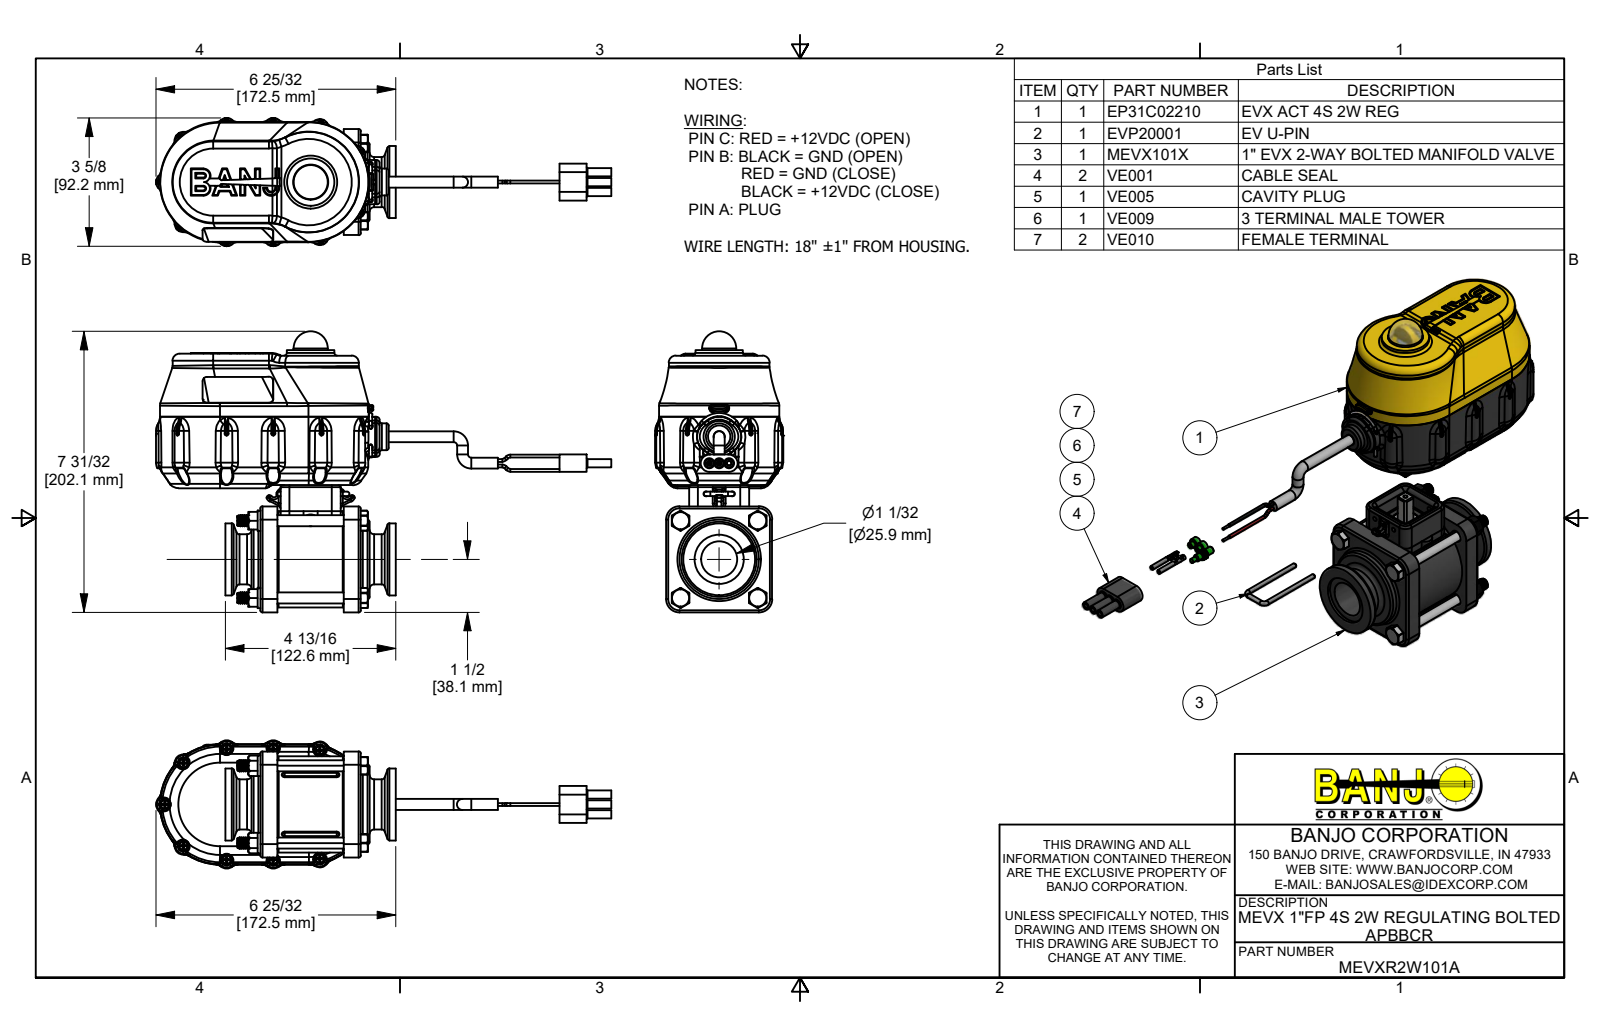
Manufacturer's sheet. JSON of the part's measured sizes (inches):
{"part_name": "MEVXR2W101A; EP31C02210; 91400A119; 95584A200 (+8 more)", "step_written_by": "Autodesk Inventor 2019 (AUTOMOTIVE_DESIGN)", "units": "inches", "bodies": {"solids": 101, "faces": 12714, "planar": 3569, "cylindrical": 3449, "other": 5696}, "overall_size": [12.901, 7.957, 3.63], "volume_in3": 51.5, "surface_area_in2": 591.9, "round_holes": [[0.15, 13], [0.095, 11], [0.107, 4], [0.126, 4], [0.136, 4], [0.17, 4], [0.252, 4], [0.322, 4], [0.35, 4], [0.135, 3], [0.14, 3], [0.243, 3]], "round_bosses_or_shafts": [[0.268, 60], [0.25, 17], [0.14, 11], [0.108, 11], [0.085, 11], [0.08, 10], [0.313, 5], [0.583, 4]], "partial_cylinders_radius": [[0.04, 147], [0.02, 83], [0.01, 56], [0.06, 46], [0.005, 43], [0.03, 32], [0.08, 28], [0.1, 22]], "face_to_face_distances": [0.1, 2.565, 1.685, 0.78, 2.465, 0.055, 0.48, 0.165, 0.88, 0.035], "hole_center_spacings": [1.283, 1.547, 2.188, 0.874, 0.946, 1.662, 1.891, 2.73]}
